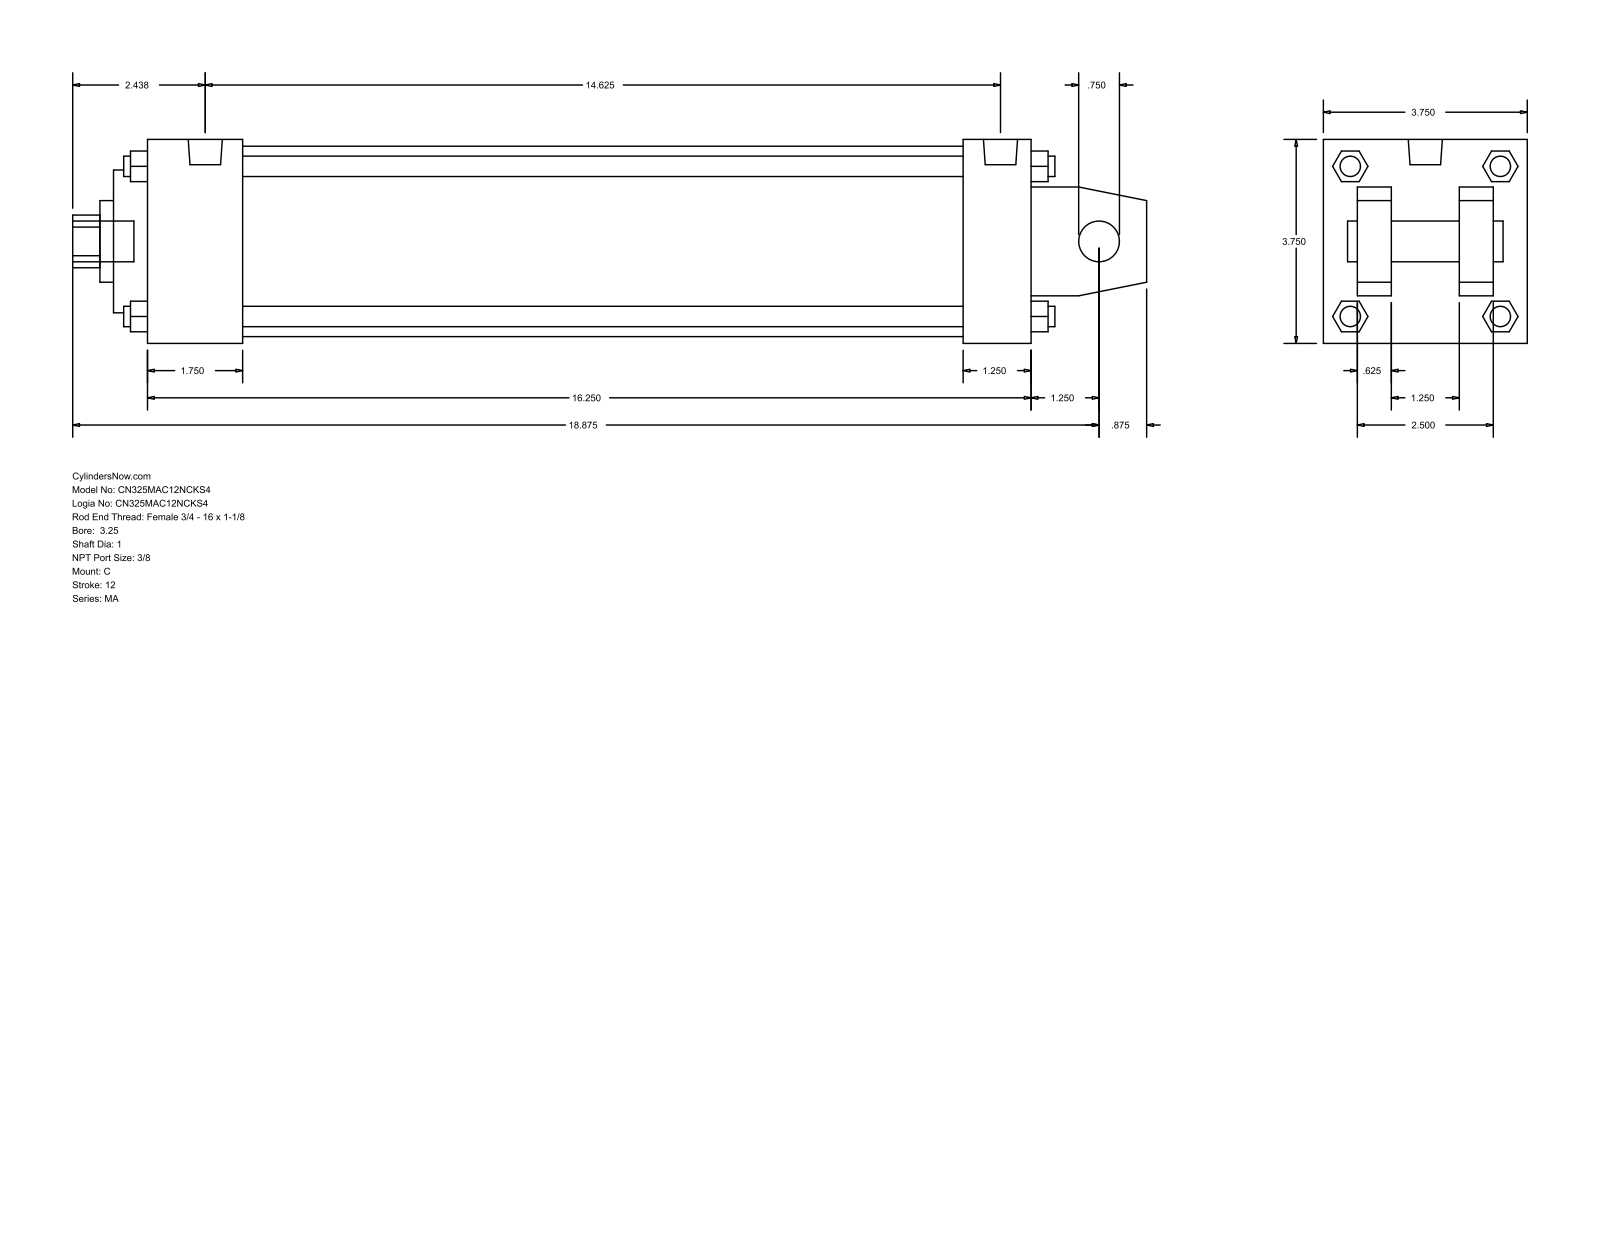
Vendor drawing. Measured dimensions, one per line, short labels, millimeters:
name: MA_C__0325_1
written by: GSSL Pune (CONFIG_CONTROL_DESIGN)
unit: mm
bodies: 0 solids, 141 faces (109 planar, 32 cylindrical, 0 other)
size: 501.65 × 95.25 × 95.25
holes: 1× ⌀19.05, 1× ⌀25.4, 1× ⌀38.1, 1× ⌀66.67, 1× ⌀88.9
bosses: 4× ⌀11.11, 4× ⌀9.53, 2× ⌀15.93, 1× ⌀19.05
rounds: 1× R12.29
face distances: 95.24, 15.87, 63.5, 412.76, 31.74, 79.37, 47.63, 381.01, 31.75, 44.46
